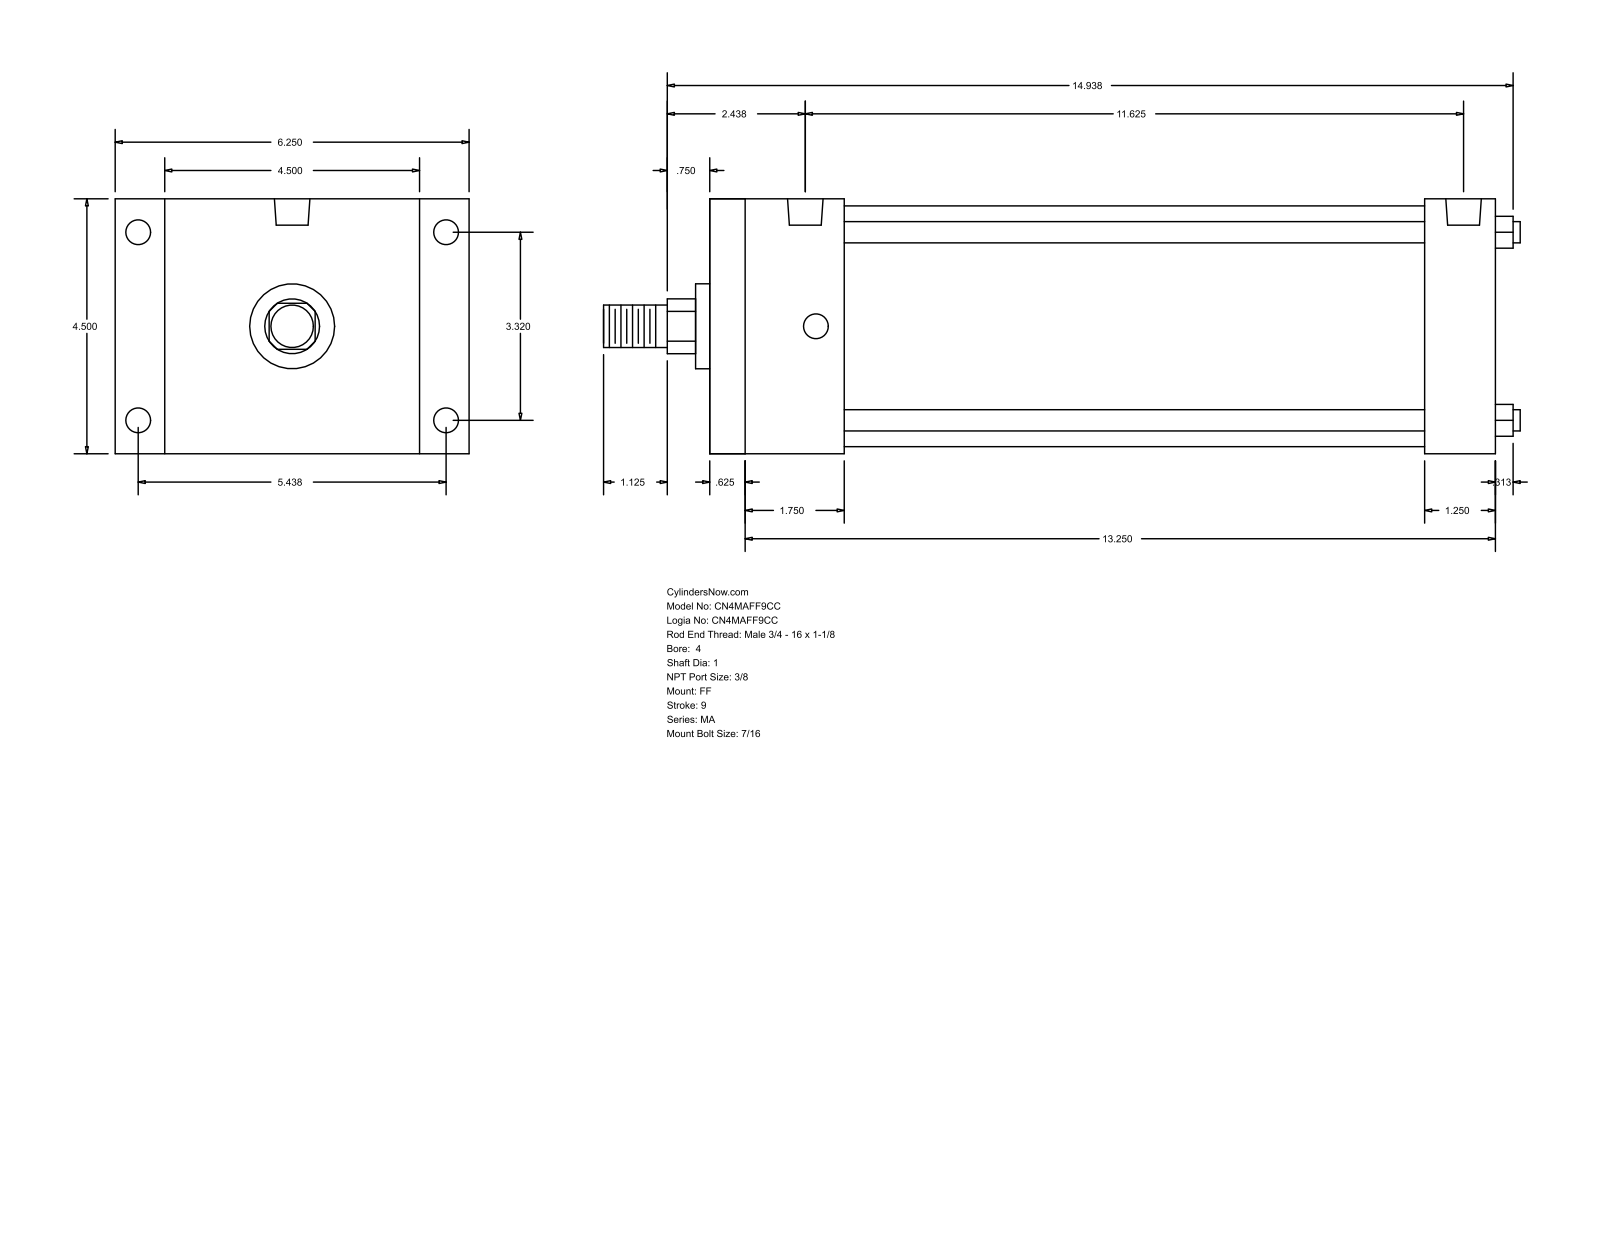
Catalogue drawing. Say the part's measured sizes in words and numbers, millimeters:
The part is named "MA_FF__0400_1". Its 3-D file was written by "GSSL Pune (CONFIG_CONTROL_DESIGN)". It is 0 solids with 92 faces: 64 planar, 28 cylindrical and 0 other. Overall it measures 411.16 by 158.75 by 114.3 millimeters. Round holes: 8 of diameter 11.11, 2 of diameter 15.93. Round bosses or shafts: 4 of diameter 9.53, 1 of diameter 107.95, 1 of diameter 38.1, 1 of diameter 25.4, 1 of diameter 19.05. Partial cylindrical surfaces (rounded edges, fillets, slot ends): 1 of radius 12.29. The main face-to-face distances are 114.3, 352.43, 15.87, 336.56, 22.23, 136.53, 320.68, 304.81, 31.75, 60.33. The hole center spacings are 4.76, 84.32, 138.12, 161.82, 285.76, 290.52, 295.28.
